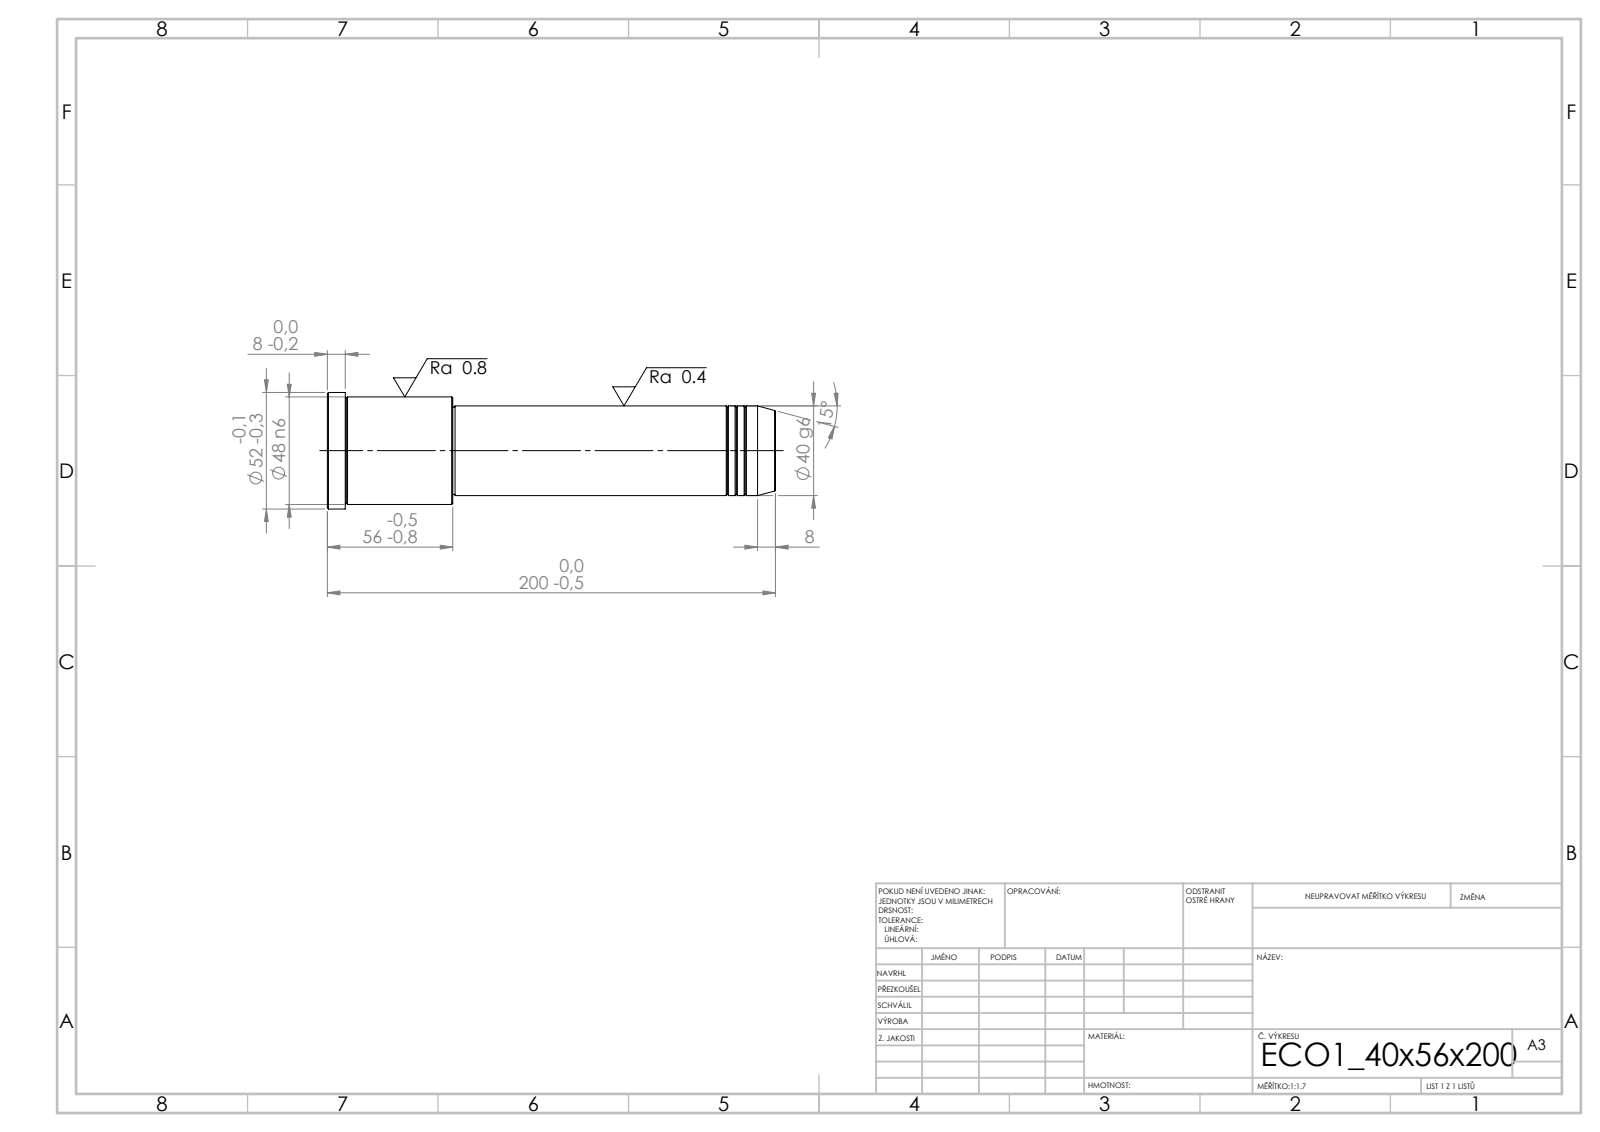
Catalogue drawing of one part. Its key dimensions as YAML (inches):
step_written_by: "SolidWorks 2019 (CONFIG_CONTROL_DESIGN)"
units: inches
bodies: {solids: 1, faces: 43, planar: 5, cylindrical: 14, other: 24}
overall_size: [7.874, 2.047, 2.047]
volume: 17.3
surface_area: 47.92
round_bosses_or_shafts:
  - {diameter: 2.047, count: 1}
  - {diameter: 1.89, count: 1}
  - {diameter: 1.575, count: 1}
  - {diameter: 1.535, count: 1}
face_to_face_distances: [7.874, 5.669, 2.205, 7.559, 1.89, 0.315, 5.63, 0.039, 1.929, 2.244]
